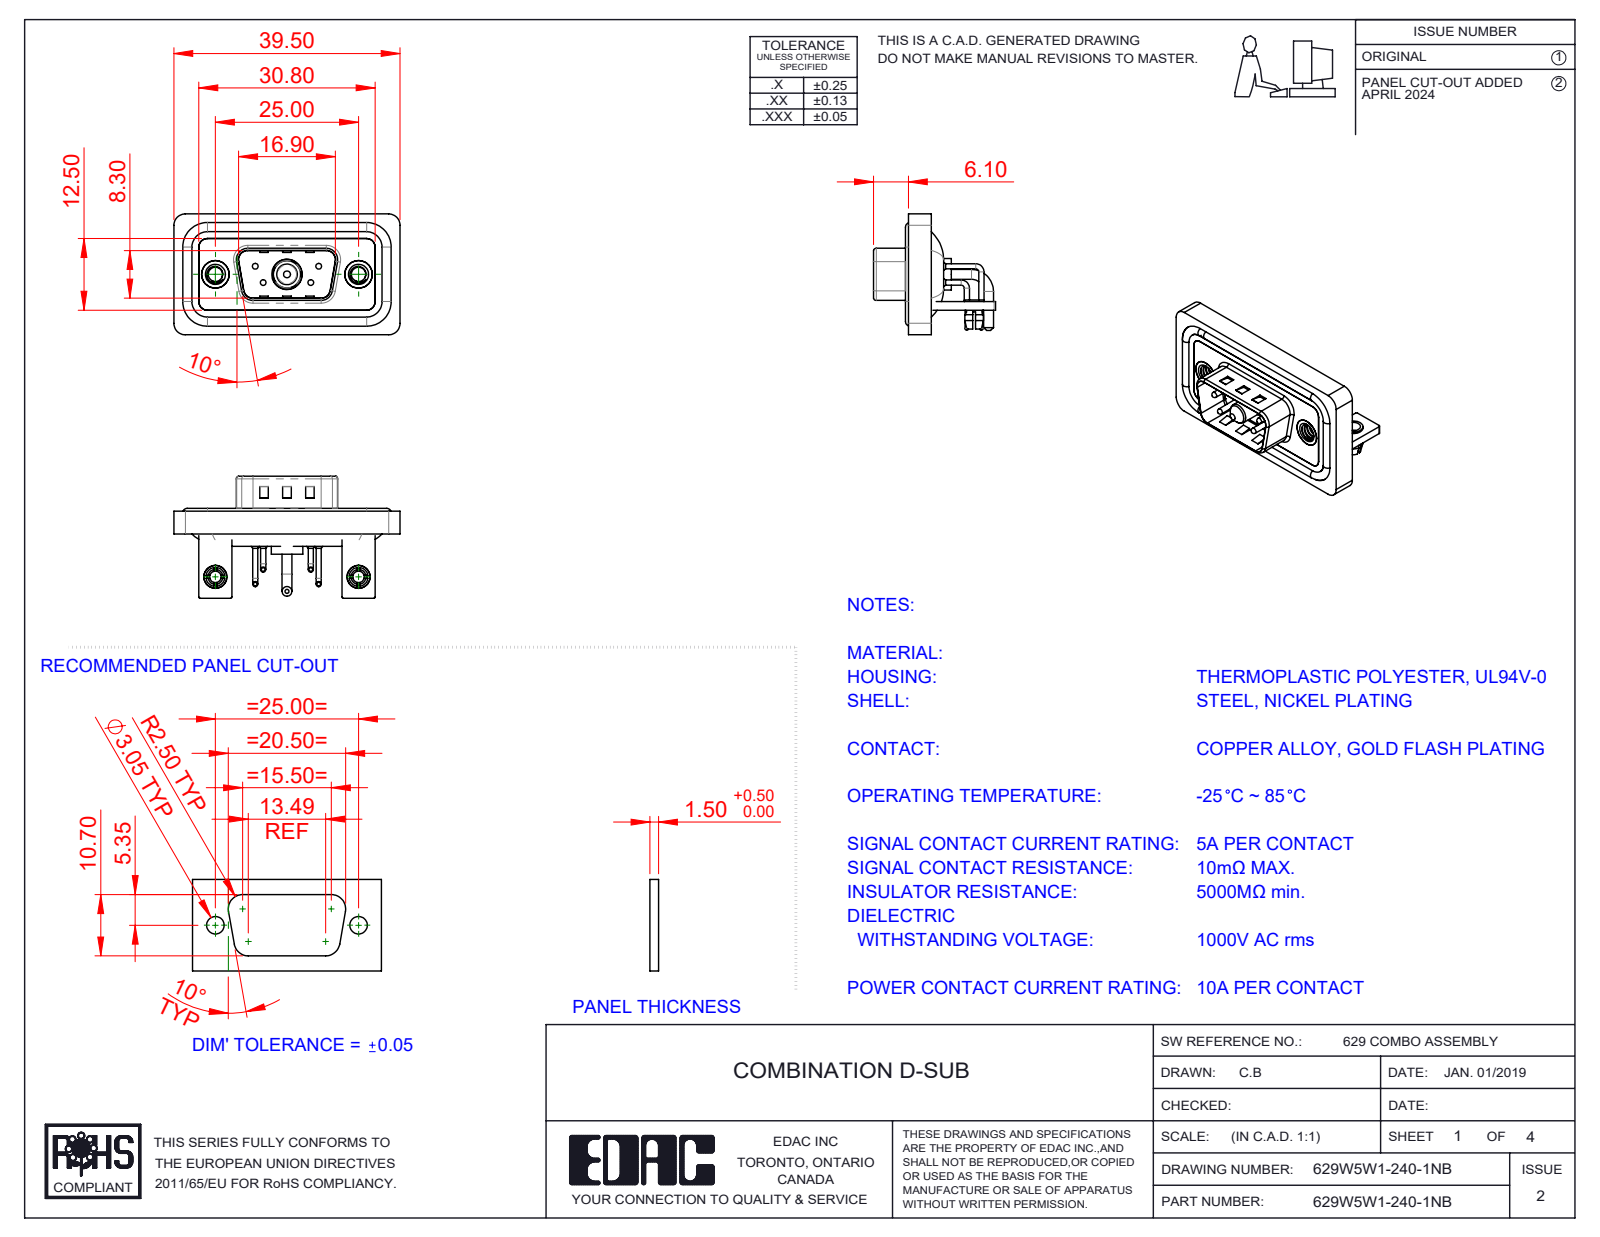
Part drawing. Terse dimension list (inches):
name: 629Combo Waterproof Housing_09 Contacts; 629Combo Contact Row 2; 629Combo Stabilizer Bracket; 629Combo Housing_5W1 (+7 more)
written by: SolidWorks 2023 (CONFIG_CONTROL_DESIGN)
unit: in
bodies: 17 solids, 1024 faces (479 planar, 395 cylindrical, 150 other)
size: 1.555 × 0.839 × 0.831
volume: 0.288 in³; area: 12.26 in²
holes: 6× ⌀0.079, 4× ⌀0.03, 4× ⌀0.063, 4× ⌀0.098, 2× ⌀0.126, 2× ⌀0.157, 2× ⌀0.189, 2× ⌀0.197, 1× ⌀0.191, 1× ⌀0.209
bosses: 8× ⌀0.035, 4× ⌀0.063, 4× ⌀0.059, 4× ⌀0.039, 4× ⌀0.026, 2× ⌀0.193, 2× ⌀0.157, 2× ⌀0.134
rounds: 19× R0.079, 18× R0.059, 16× R0.01, 9× R0.02, 8× R0.063, 4× R0.024, 4× R0.026, 4× R0.035
face distances: 0.016, 0.059, 0.031, 0.114, 0.043, 0.083, 0.047, 0.063, 0.098, 0.146
hole spacings: 0.124, 0.225, 0.28, 0.492, 0.713, 0.984, 0.173, 0.173
